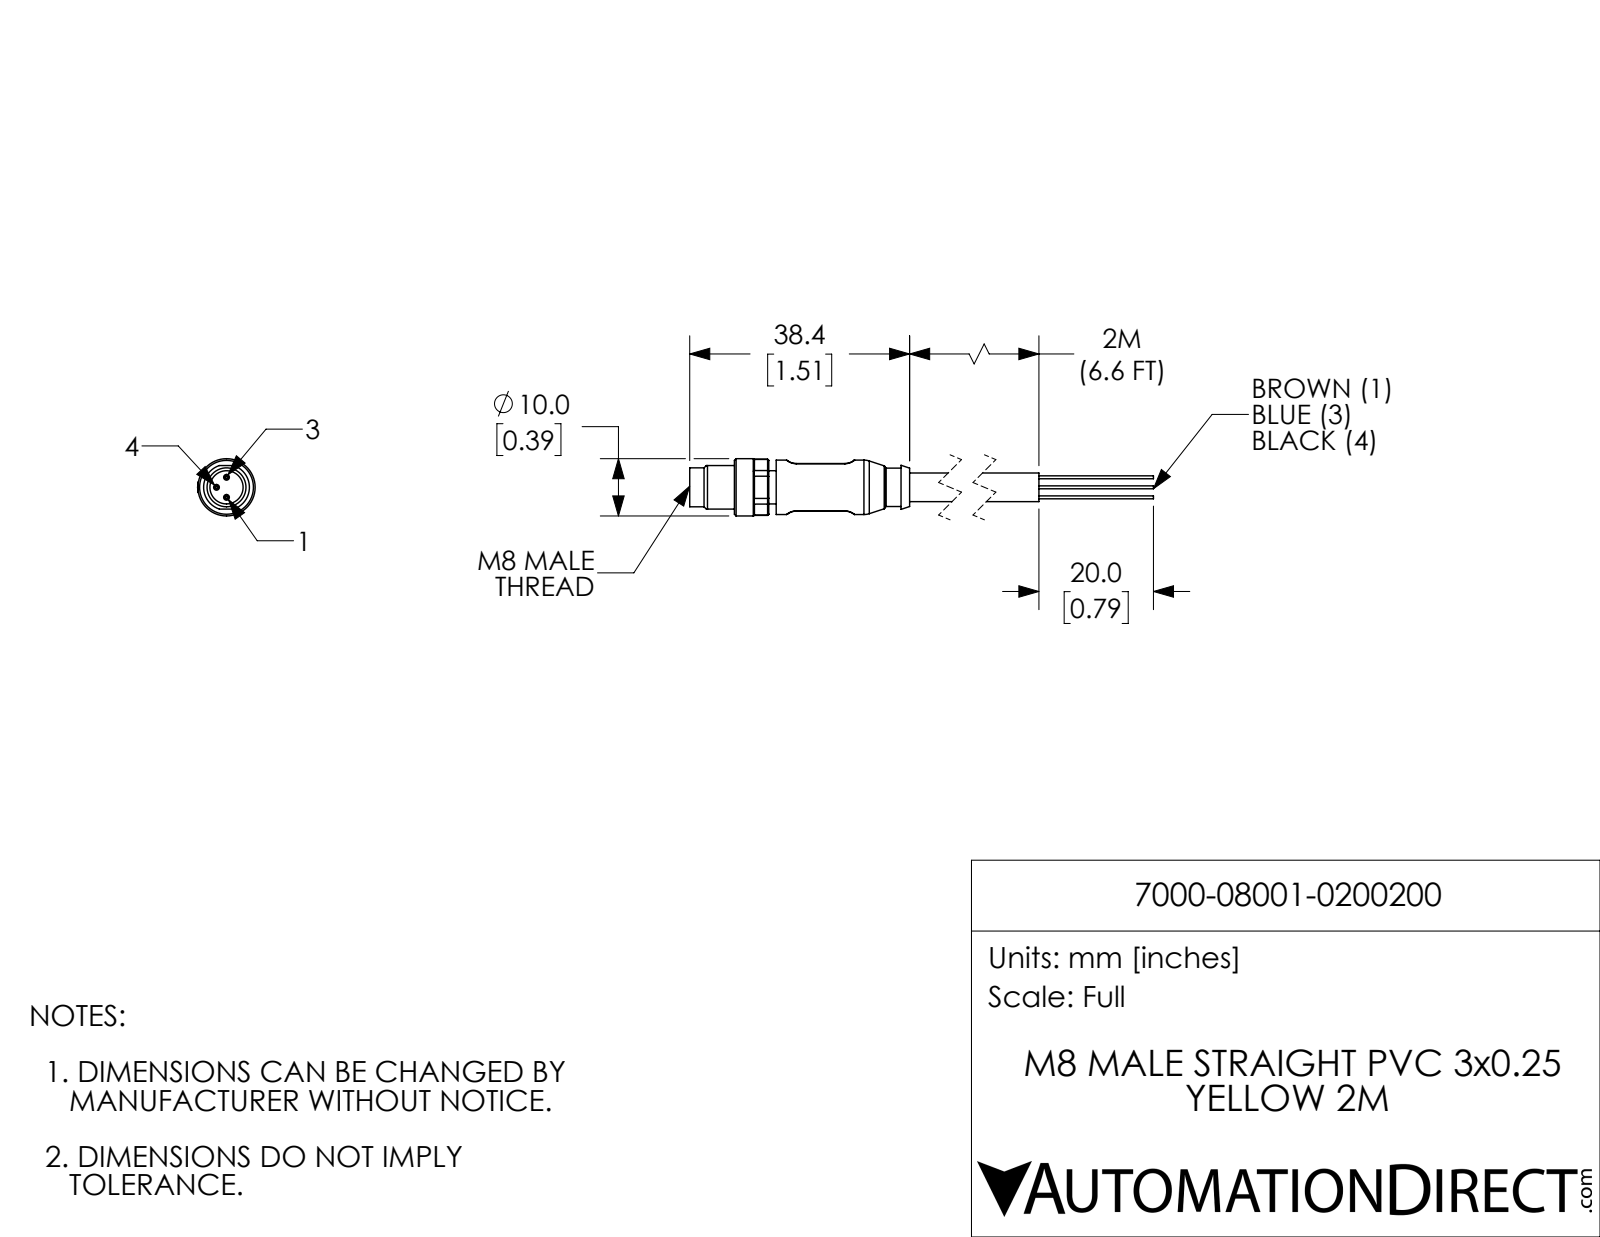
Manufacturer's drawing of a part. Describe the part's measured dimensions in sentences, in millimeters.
The part is named "7000-08001-0200200". Its 3-D file was written by "SolidWorks 2017 (AUTOMOTIVE_DESIGN)". It is 4 solids with 119 faces: 41 planar, 44 cylindrical and 34 other. Overall it measures 78.4 by 10.05 by 10 millimeters. Its volume is 2 535 cubic millimeters and its surface area 1 801 square millimeters. Round holes: 1 of diameter 5.8. Round bosses or shafts: 3 of diameter 1, 3 of diameter 0.51, 1 of diameter 10, 1 of diameter 9.5, 1 of diameter 8, 1 of diameter 6.8, 1 of diameter 6.7, 1 of diameter 5. Partial cylindrical surfaces (rounded edges, fillets, slot ends): 4 of radius 0.2, 4 of radius 2.5, 1 of radius 4.9, 1 of radius 5.05. The main face-to-face distances are 8.3, 1.3, 9, 0.35, 7.95, 8.8, 10.1, 53.4, 44.6, 43.3.
